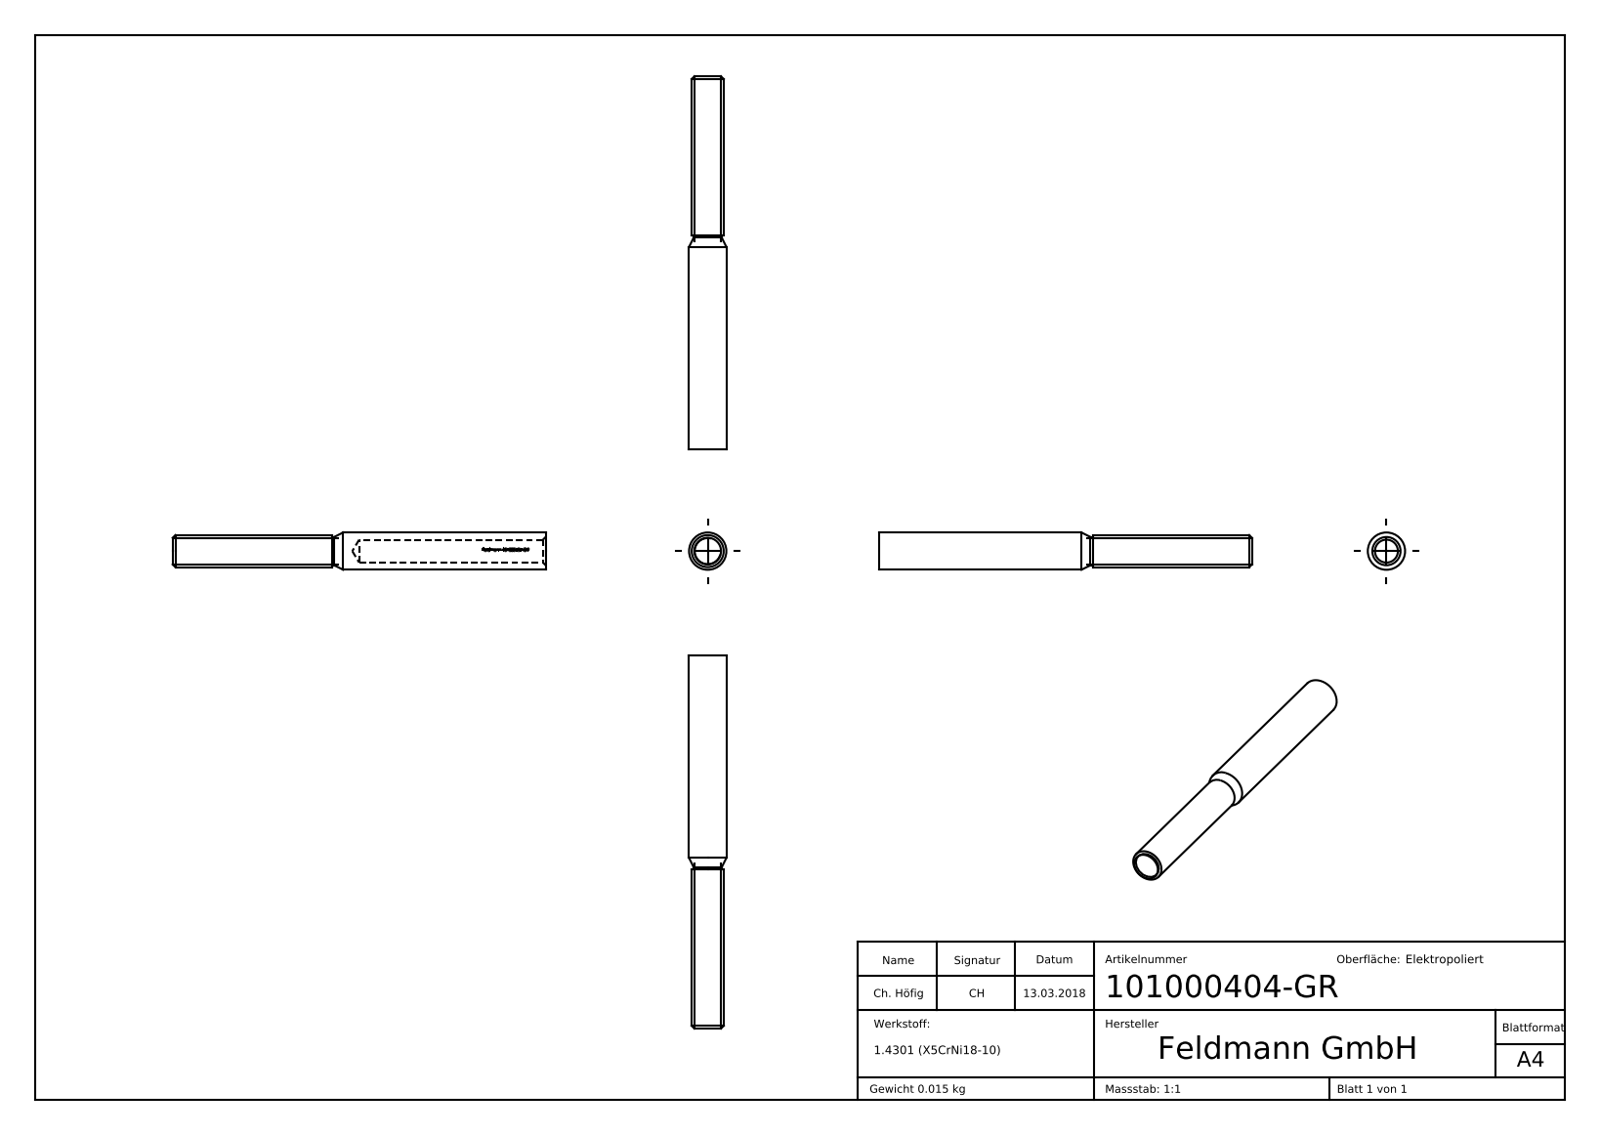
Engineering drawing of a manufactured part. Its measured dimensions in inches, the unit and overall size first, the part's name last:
Units: inches
Overall size (bounding box): 2.756 × 0.276 × 0.276
Round holes (diameter × count): ⌀0.169 ×1
Round bosses / shafts (diameter × count): ⌀0.276 ×1, ⌀0.236 ×1, ⌀0.209 ×1
Partial cylindrical surfaces — rounded edges, fillets, slot ends (radius × count): R0.089 ×1
Main face-to-face distances: 2.756, 1.579, 1.177, 0.032, 0.153, 0.155, 0.014, 0.1, 0.254, 0.327
Volume: 0.113 in³ · Surface area: 3.078 in²
Bodies: 1 solid, 268 faces (114 planar, 39 cylindrical, 115 other)
Part name (STEP PRODUCT): 101000404-GR
STEP written by: SolidWorks 2015 (CONFIG_CONTROL_DESIGN)
